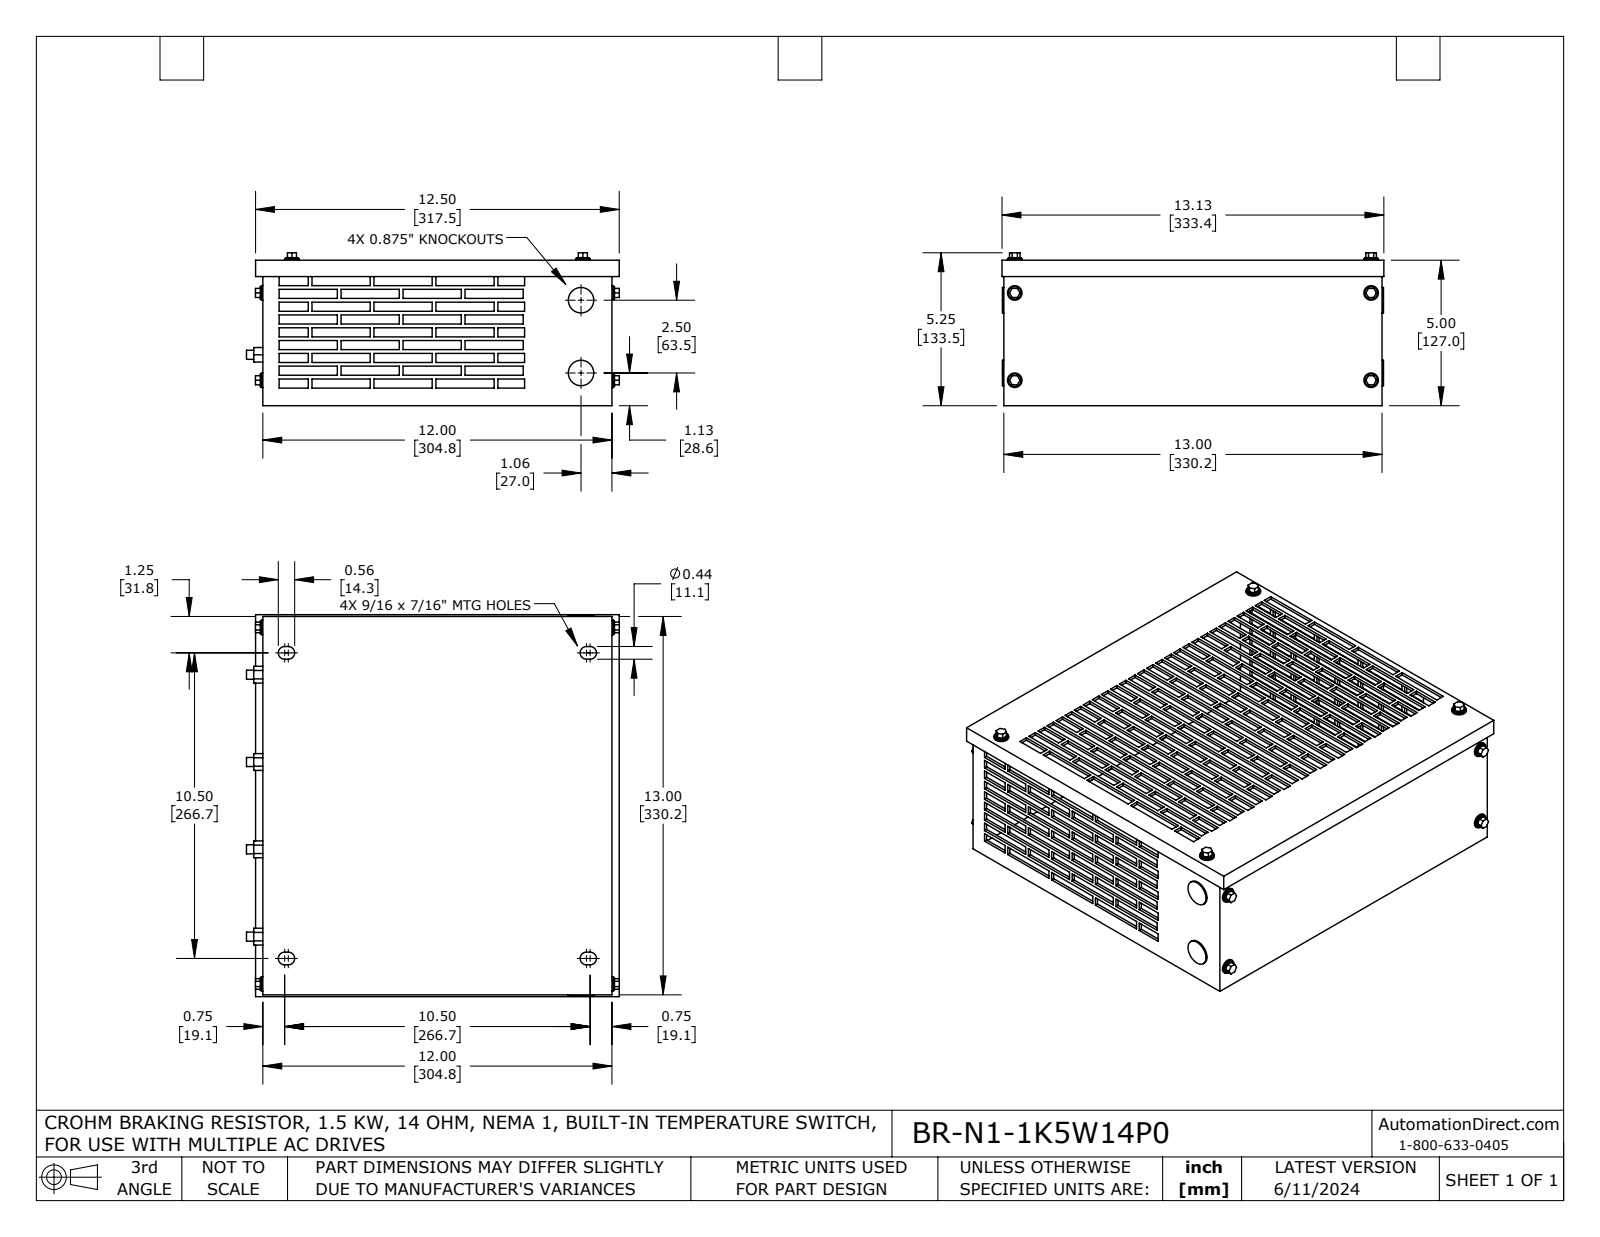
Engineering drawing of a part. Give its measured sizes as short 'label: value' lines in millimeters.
name: BR-N1-1K5W14P0
written by: SolidWorks 2021 (AUTOMOTIVE_DESIGN)
unit: mm
bodies: 33 solids, 1136 faces (1032 planar, 104 cylindrical, 0 other)
size: 333.4 × 325.6 × 133.5
volume: 750 400 mm³; area: 651 600 mm²
holes: 8× ⌀6.4, 2× ⌀19.1
bosses: 8× ⌀12.7, 8× ⌀11.1, 4× ⌀8, 2× ⌀22.2
rounds: 8× R5.6
face distances: 2.5, 124.5, 302.3, 127, 121.9, 304.8, 327.7, 299.7, 330.2, 325.1
hole spacings: 311.2, 76.2, 254, 320.3, 401.7, 63.5
